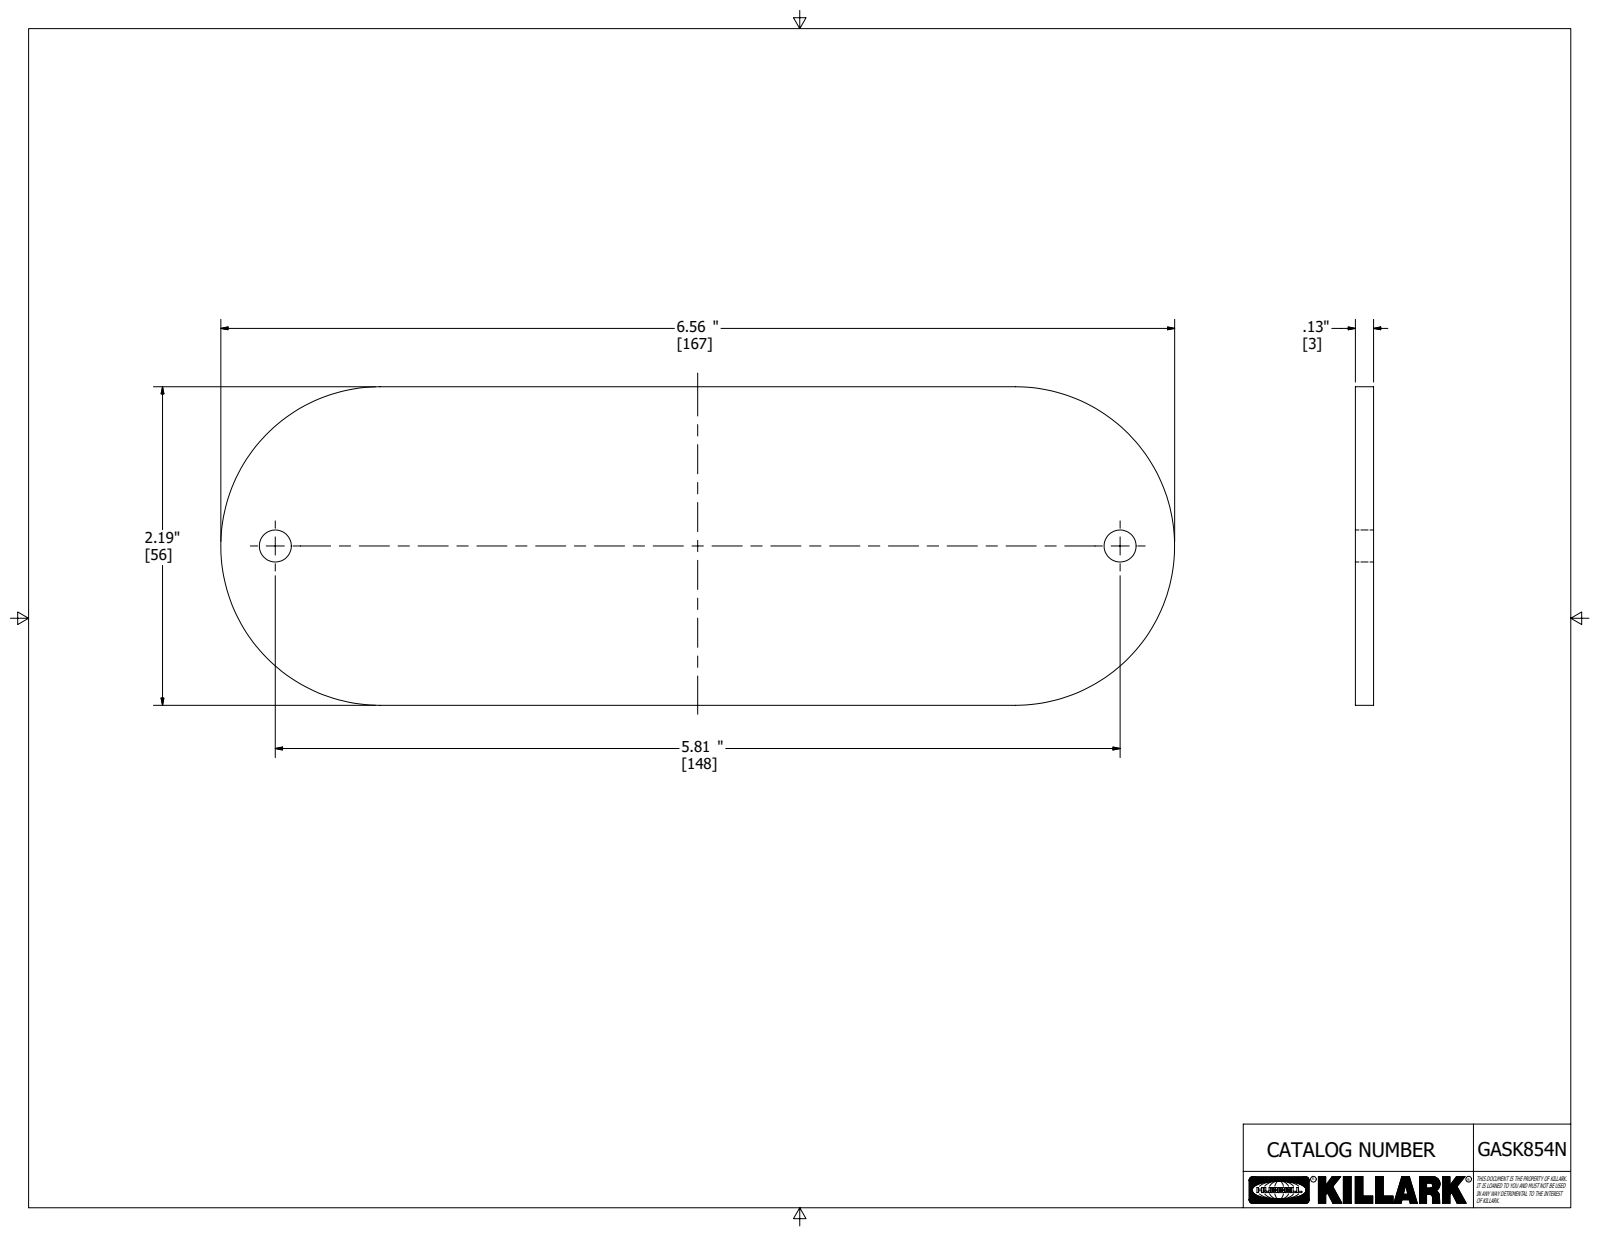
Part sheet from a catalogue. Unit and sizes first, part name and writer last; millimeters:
Units: millimetres
Overall size (bounding box): 166.6 × 55.6 × 3.2
Round holes (diameter × count): ⌀5.6 ×2
Partial cylindrical surfaces — rounded edges, fillets, slot ends (radius × count): R27.8 ×2
Main face-to-face distances: 3.2, 55.6
Hole centre spacings: 147.6
Volume: 27 170 mm³ · Surface area: 18 480 mm²
Bodies: 1 solid, 8 faces (4 planar, 4 cylindrical, 0 other)
Part name (STEP PRODUCT): 21779
STEP written by: Autodesk Inventor 2018 (AUTOMOTIVE_DESIGN)
